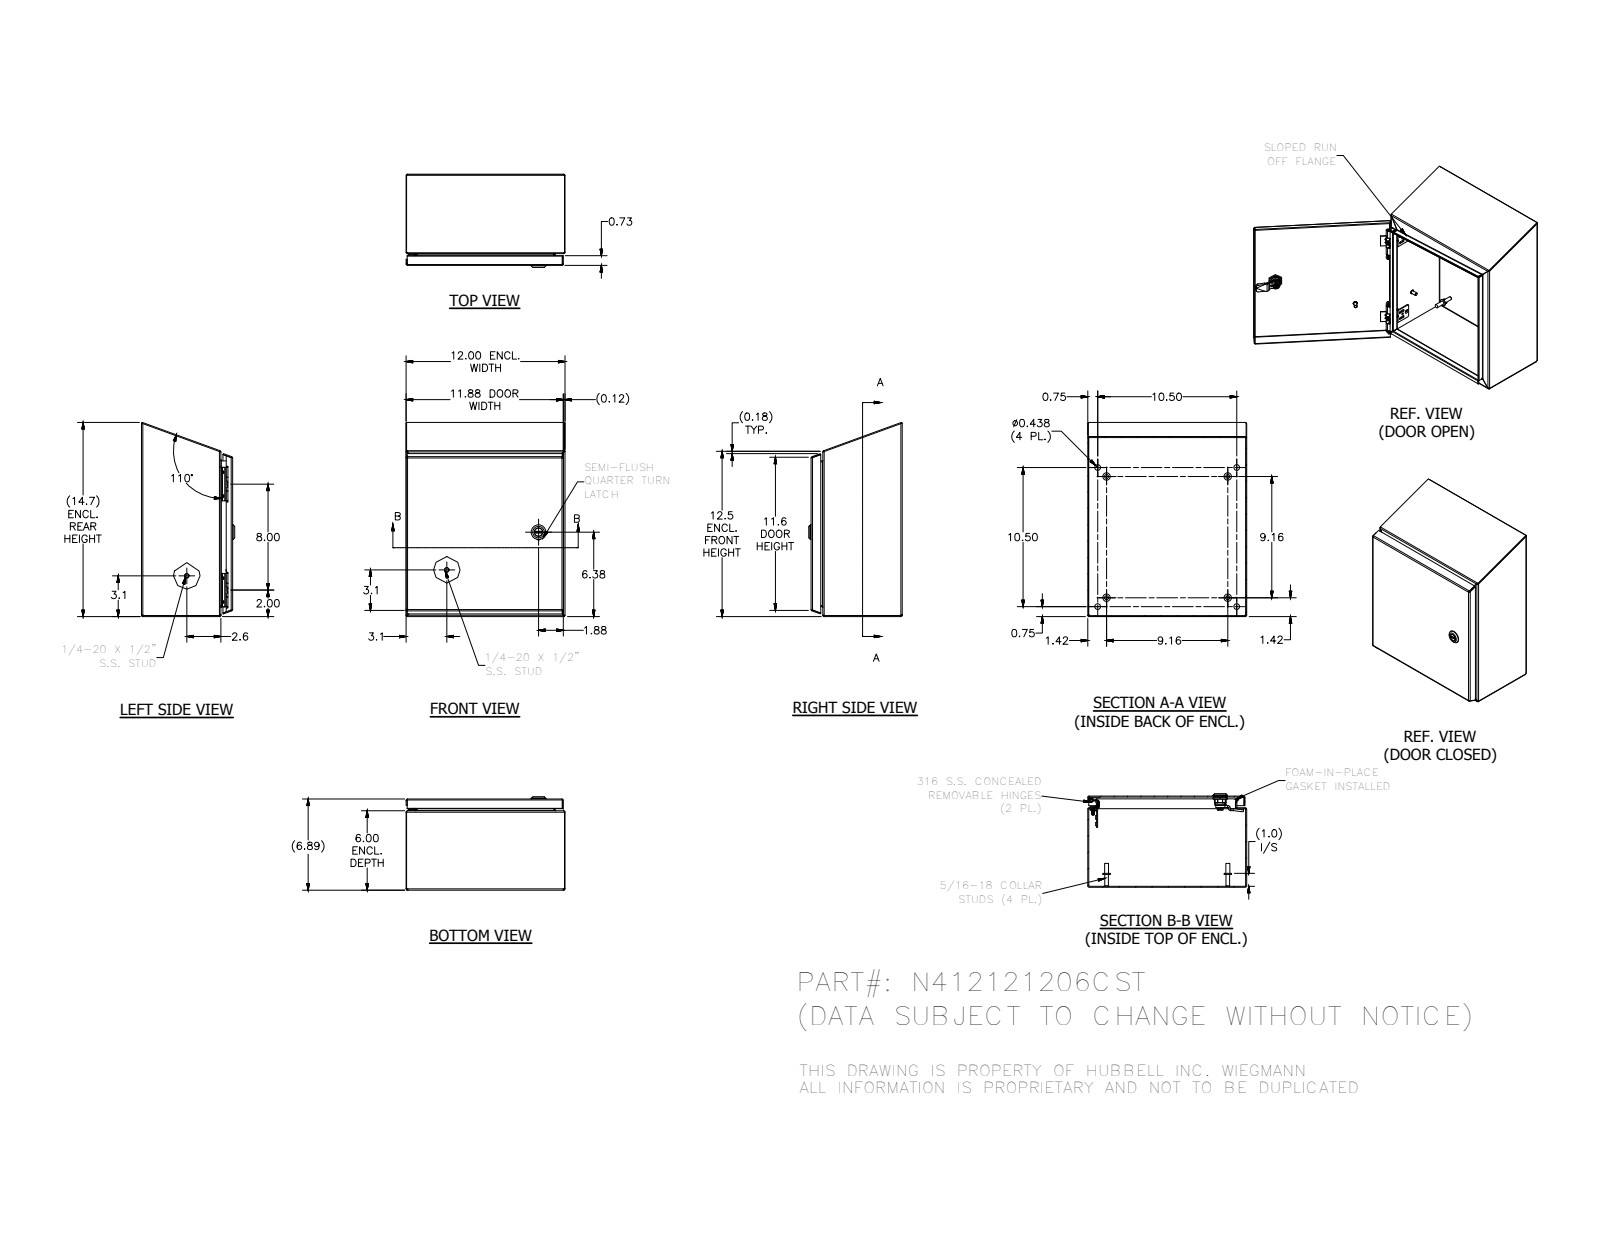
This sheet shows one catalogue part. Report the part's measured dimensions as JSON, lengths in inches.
{"part_name": "N412121206CST", "step_written_by": "SolidWorks 2018 (AUTOMOTIVE_DESIGN)", "units": "inches", "bodies": {"solids": 36, "faces": 1520, "planar": 567, "cylindrical": 552, "other": 401}, "overall_size": [14.663, 12, 7.044], "volume_in3": 55.26, "surface_area_in2": 1507, "round_holes": [[0.093, 4], [0.152, 4], [0.167, 4], [0.172, 4], [0.187, 4], [0.437, 4], [0.156, 3], [0.187, 1], [0.197, 1], [0.315, 1], [0.394, 1], [0.402, 1]], "round_bosses_or_shafts": [[0.25, 10], [0.563, 4], [0.36, 4], [0.32, 4], [0.3, 4], [0.275, 4], [0.256, 4], [0.164, 4]], "partial_cylinders_radius": [[0.012, 30], [0.031, 29], [0.05, 26], [0.105, 19], [0.016, 18], [0.125, 16], [0.02, 13], [0.032, 8]], "face_to_face_distances": [0.074, 6.813, 11.926, 6.739, 6.887, 11.852, 12, 0.074, 5.926, 0.887], "hole_center_spacings": [8, 10.5, 0.5, 0.656, 0.66, 1.307, 1.311, 1.965]}
